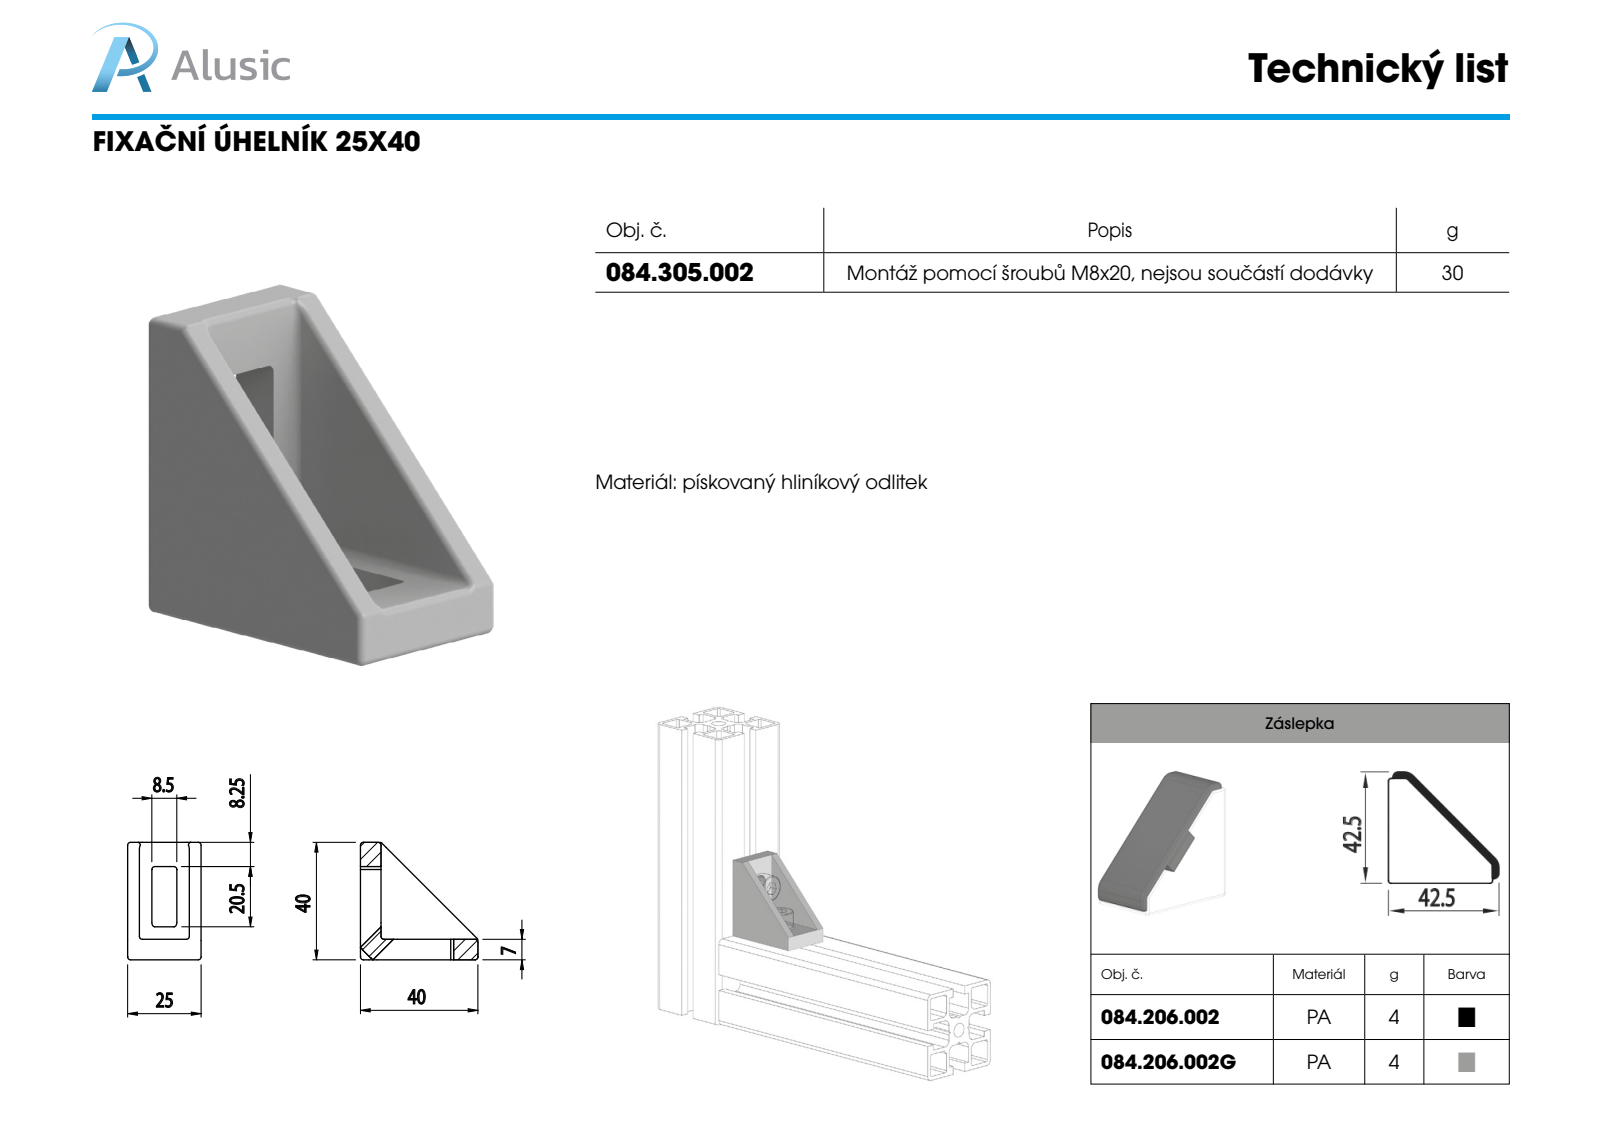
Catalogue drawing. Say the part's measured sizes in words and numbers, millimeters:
The part is named "084.305.002". Its 3-D file was written by "SolidWorks 2018 (CONFIG_CONTROL_DESIGN)". It is 1 solid with 243 faces: 52 planar, 107 cylindrical and 84 other. Overall it measures 40 by 40 by 25 millimeters. Its volume is 12 040 cubic millimeters and its surface area 7 796 square millimeters. Round bosses or shafts: 5 of diameter 4. Partial cylindrical surfaces (rounded edges, fillets, slot ends): 48 of radius 0.5, 34 of radius 1, 4 of radius 2.25. The main face-to-face distances are 4, 21, 2, 25, 16.75, 4.25, 8.25, 6.25, 14.75, 12.75.
